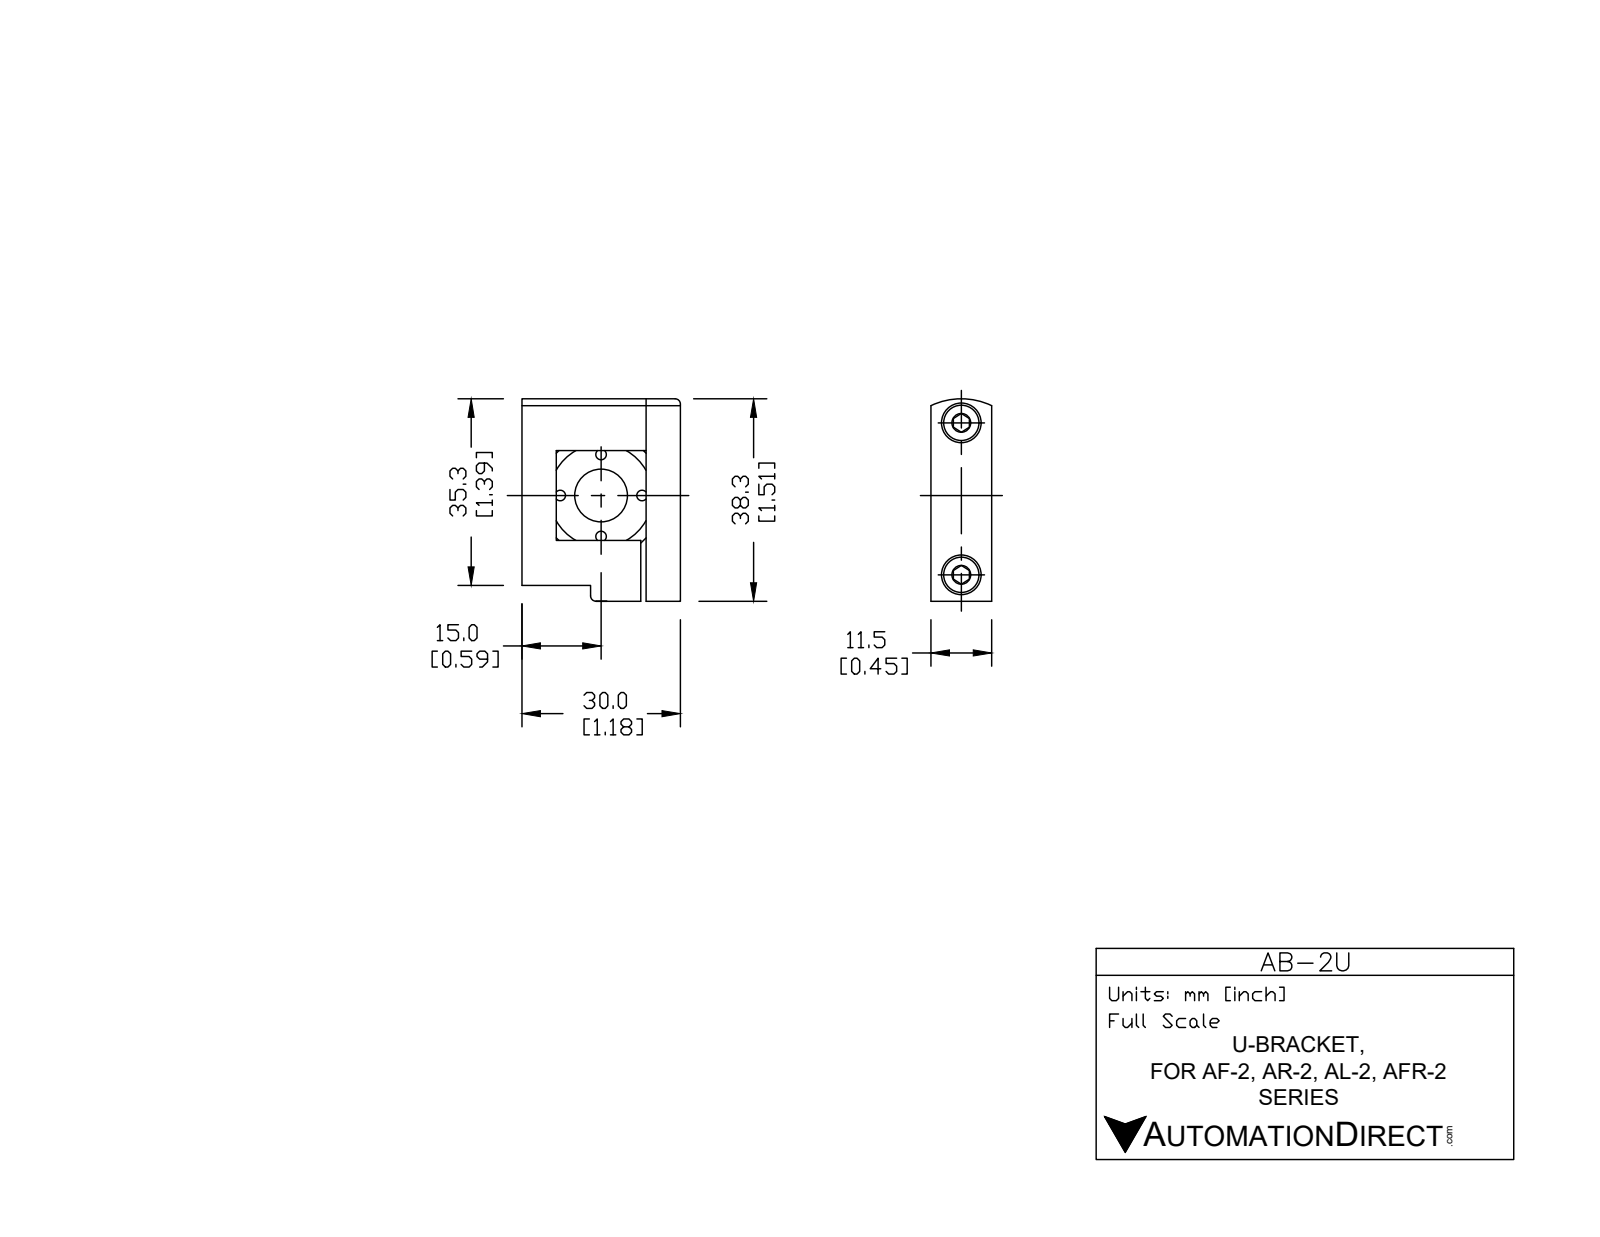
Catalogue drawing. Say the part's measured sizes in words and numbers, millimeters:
The part is named "AB-2U". Its 3-D file was written by "SolidWorks 2015 (CONFIG_CONTROL_DESIGN)". It is 3 solids with 86 faces: 54 planar, 20 cylindrical and 12 other. Overall it measures 38.3 by 30 by 11.5 millimeters. Its volume is 9 005 cubic millimeters and its surface area 5 689 square millimeters. Round holes: 2 of diameter 4.5, 2 of diameter 6.21, 1 of diameter 10. Round bosses or shafts: 2 of diameter 5.75, 2 of diameter 4. Partial cylindrical surfaces (rounded edges, fillets, slot ends): 1 of radius 1.5, 1 of radius 13.37. The main face-to-face distances are 11.5, 30, 1.5, 18.5, 5, 2, 6.5, 25, 20, 23.5. The hole center spacings are 28.75.
